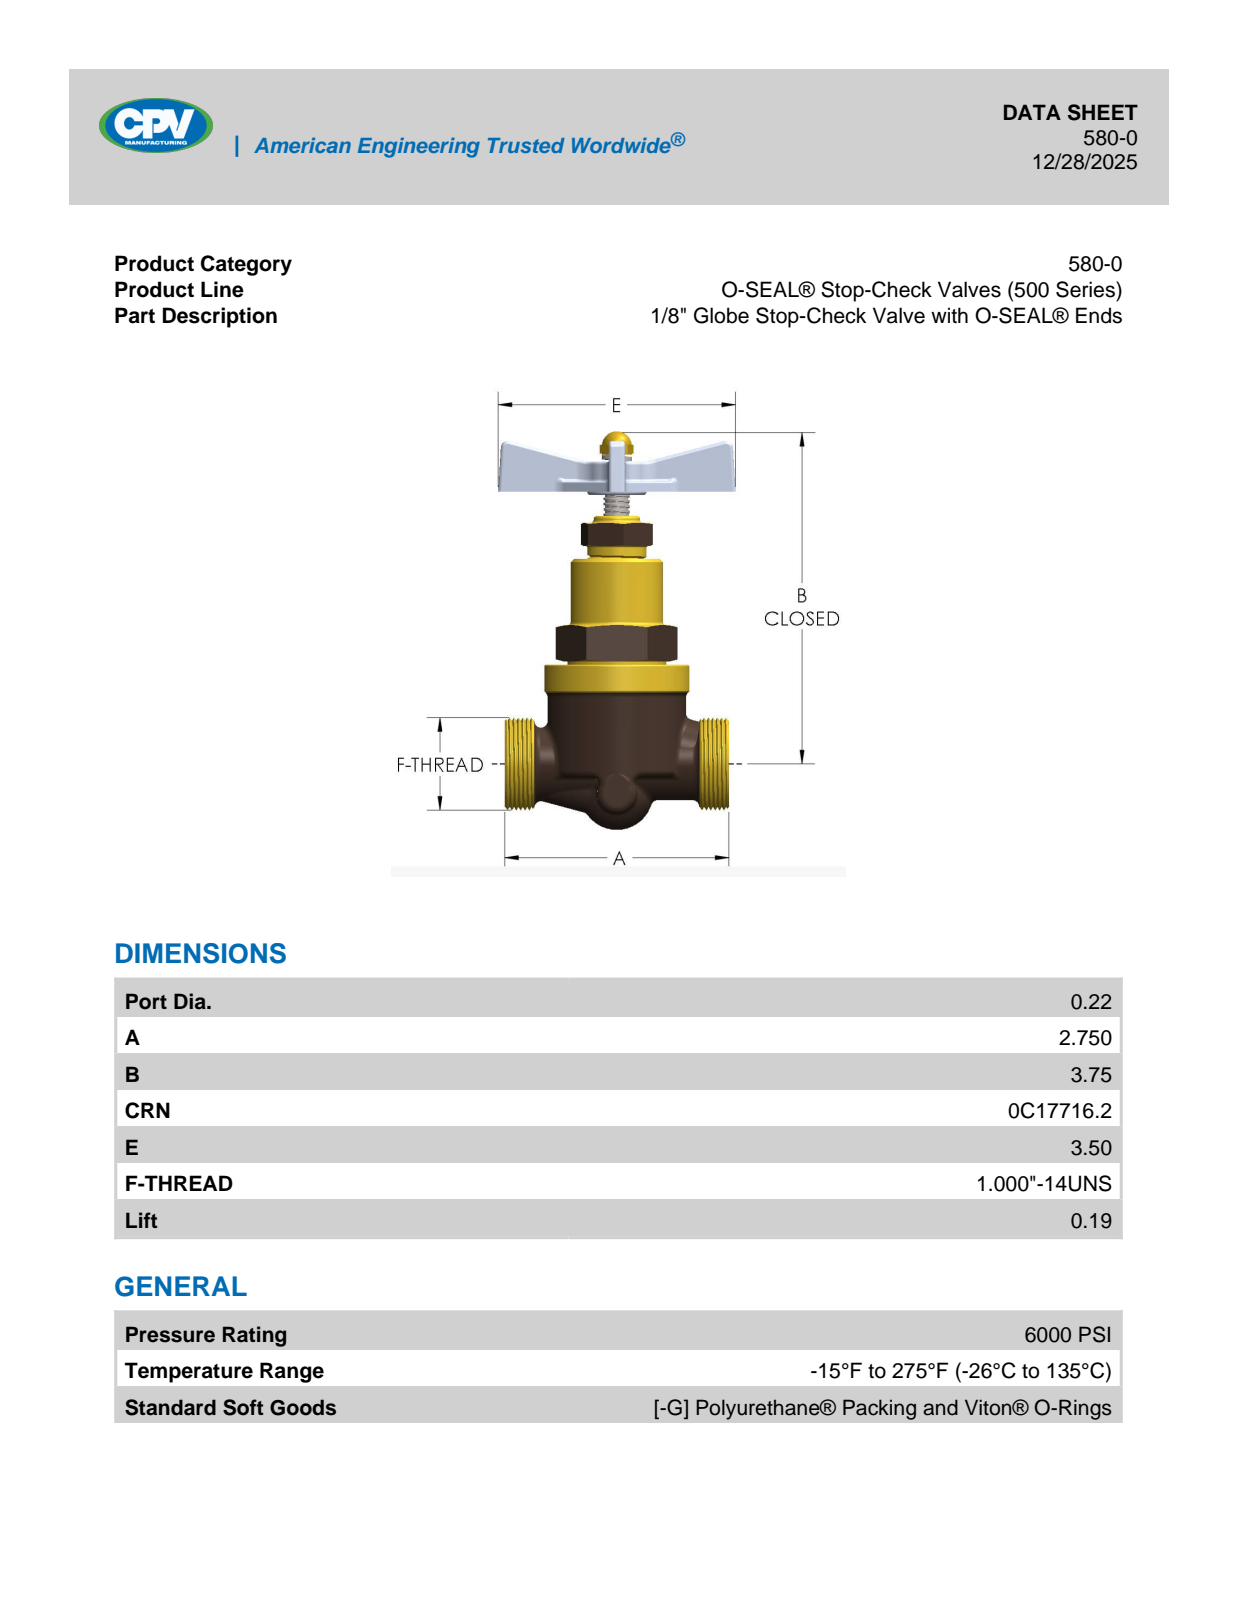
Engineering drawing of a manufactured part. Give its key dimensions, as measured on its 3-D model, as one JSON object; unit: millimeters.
{"part_name": "380-0 (14100)", "step_written_by": "SolidWorks 2018 (AUTOMOTIVE_DESIGN)", "units": "millimeters", "bodies": {"solids": 2, "faces": 700, "planar": 125, "cylindrical": 262, "other": 313}, "overall_size": [113.7, 88.9, 88.9], "volume_mm3": 112100, "surface_area_mm2": 37180, "round_holes": [[5.6, 2], [3.3, 1], [6.5, 1], [6.9, 1], [13.7, 1], [19, 1], [26.2, 1], [28.7, 1], [30.1, 1]], "round_bosses_or_shafts": [[19.1, 2], [17.4, 2], [42.9, 1], [39.7, 1], [30.1, 1], [25.7, 1], [25.4, 1], [25.3, 1]], "partial_cylinders_radius": [[3.3, 24], [0.1, 16], [1.5, 16], [2.8, 1], [6.4, 1], [8, 1], [9.7, 1], [11.8, 1]], "face_to_face_distances": [31, 7.9, 38.9, 45.1, 3.3, 48.4, 53.2, 8.1, 4.8, 12.7], "hole_center_spacings": [14.5]}
